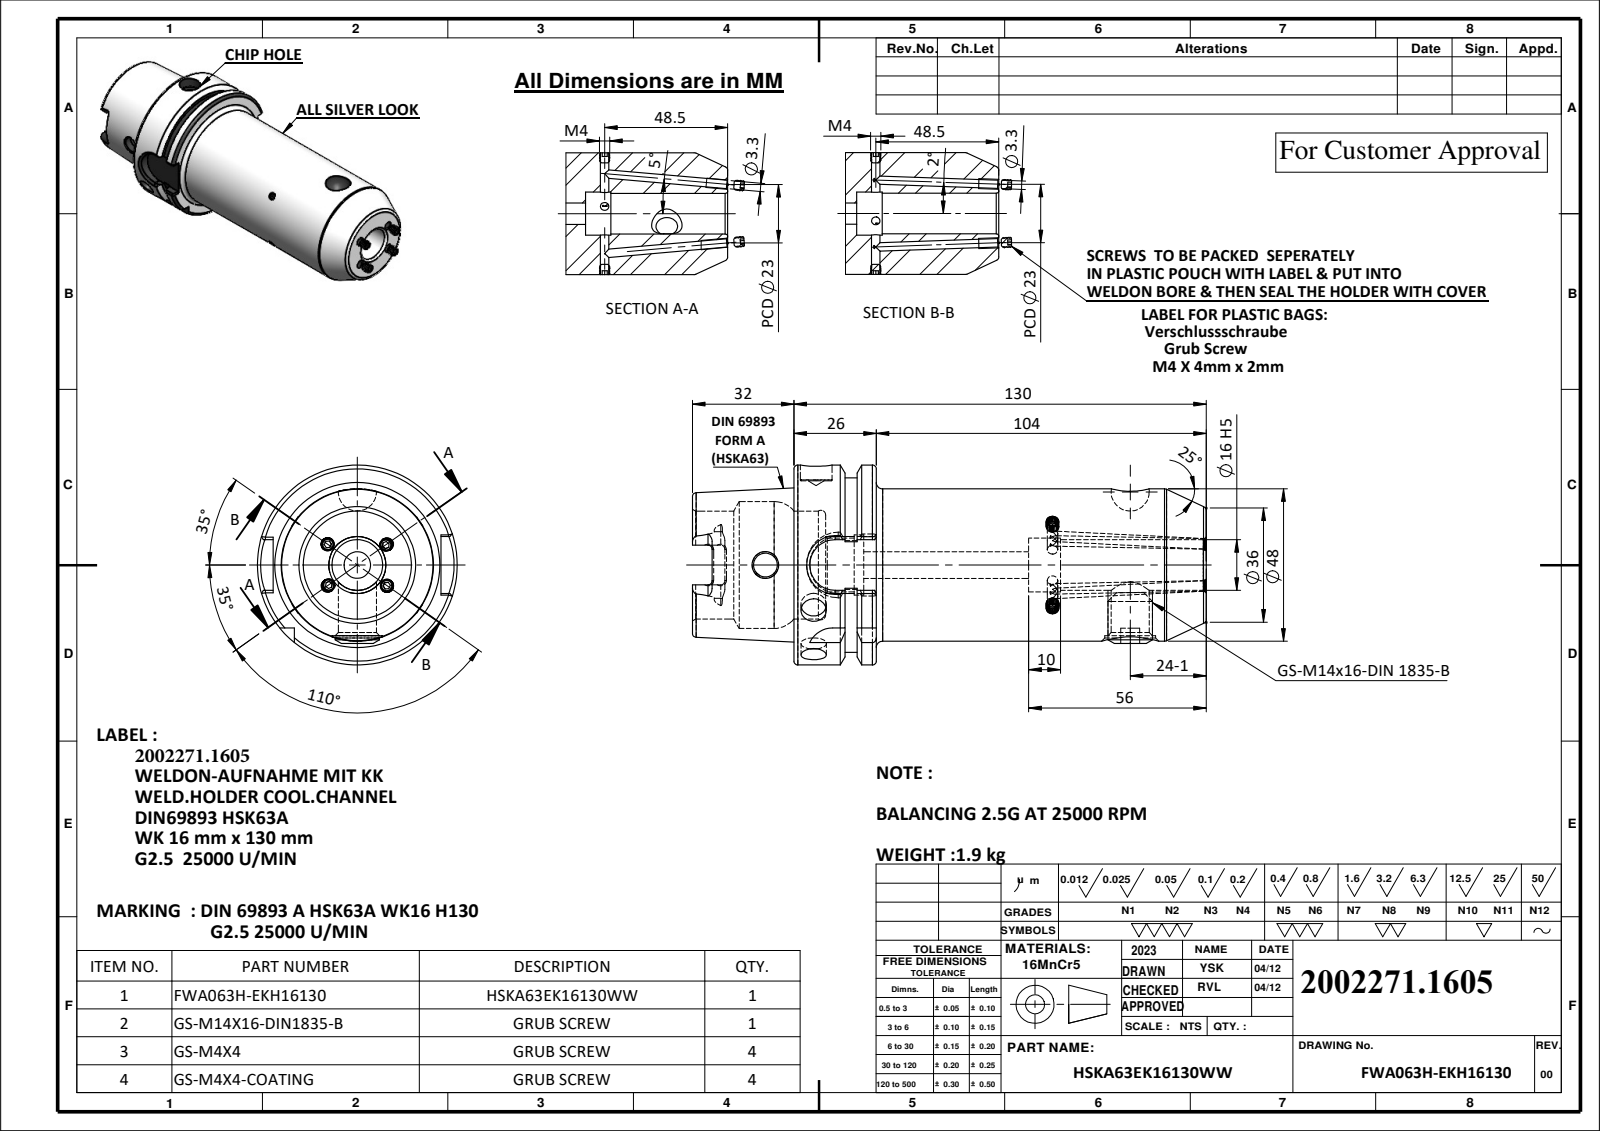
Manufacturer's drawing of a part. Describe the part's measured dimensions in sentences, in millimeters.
The part is named "HSKA63EK16130WW; GS-M4X4_DIN 913 - M4 x 4-N; GS-M14X16-DIN1835-B_ISO 4026 - M12 x 12-N; GS-M4X4-COATING_DIN 913 - M4 x 4-N (+1 more)". Its 3-D file was written by "SolidWorks 2023 (CONFIG_CONTROL_DESIGN)". It is 10 solids with 610 faces: 133 planar, 165 cylindrical and 312 other. Overall it measures 168.6 by 63 by 63 millimeters. Its volume is 247 400 cubic millimeters and its surface area 45 893 square millimeters. Round holes: 8 of diameter 3.3, 2 of diameter 8, 2 of diameter 16, 1 of diameter 7.5, 1 of diameter 8.4, 1 of diameter 10, 1 of diameter 12, 1 of diameter 17, 1 of diameter 19, 1 of diameter 34, 1 of diameter 40. Round bosses or shafts: 8 of diameter 4, 1 of diameter 63, 1 of diameter 55, 1 of diameter 48, 1 of diameter 14. Partial cylindrical surfaces (rounded edges, fillets, slot ends): 6 of radius 1.3, 4 of radius 2.88, 2 of radius 8, 1 of radius 9. The main face-to-face distances are 25.95, 130, 104.05, 10, 15.95, 120, 32, 42, 57.95, 162. The hole center spacings are 99.
